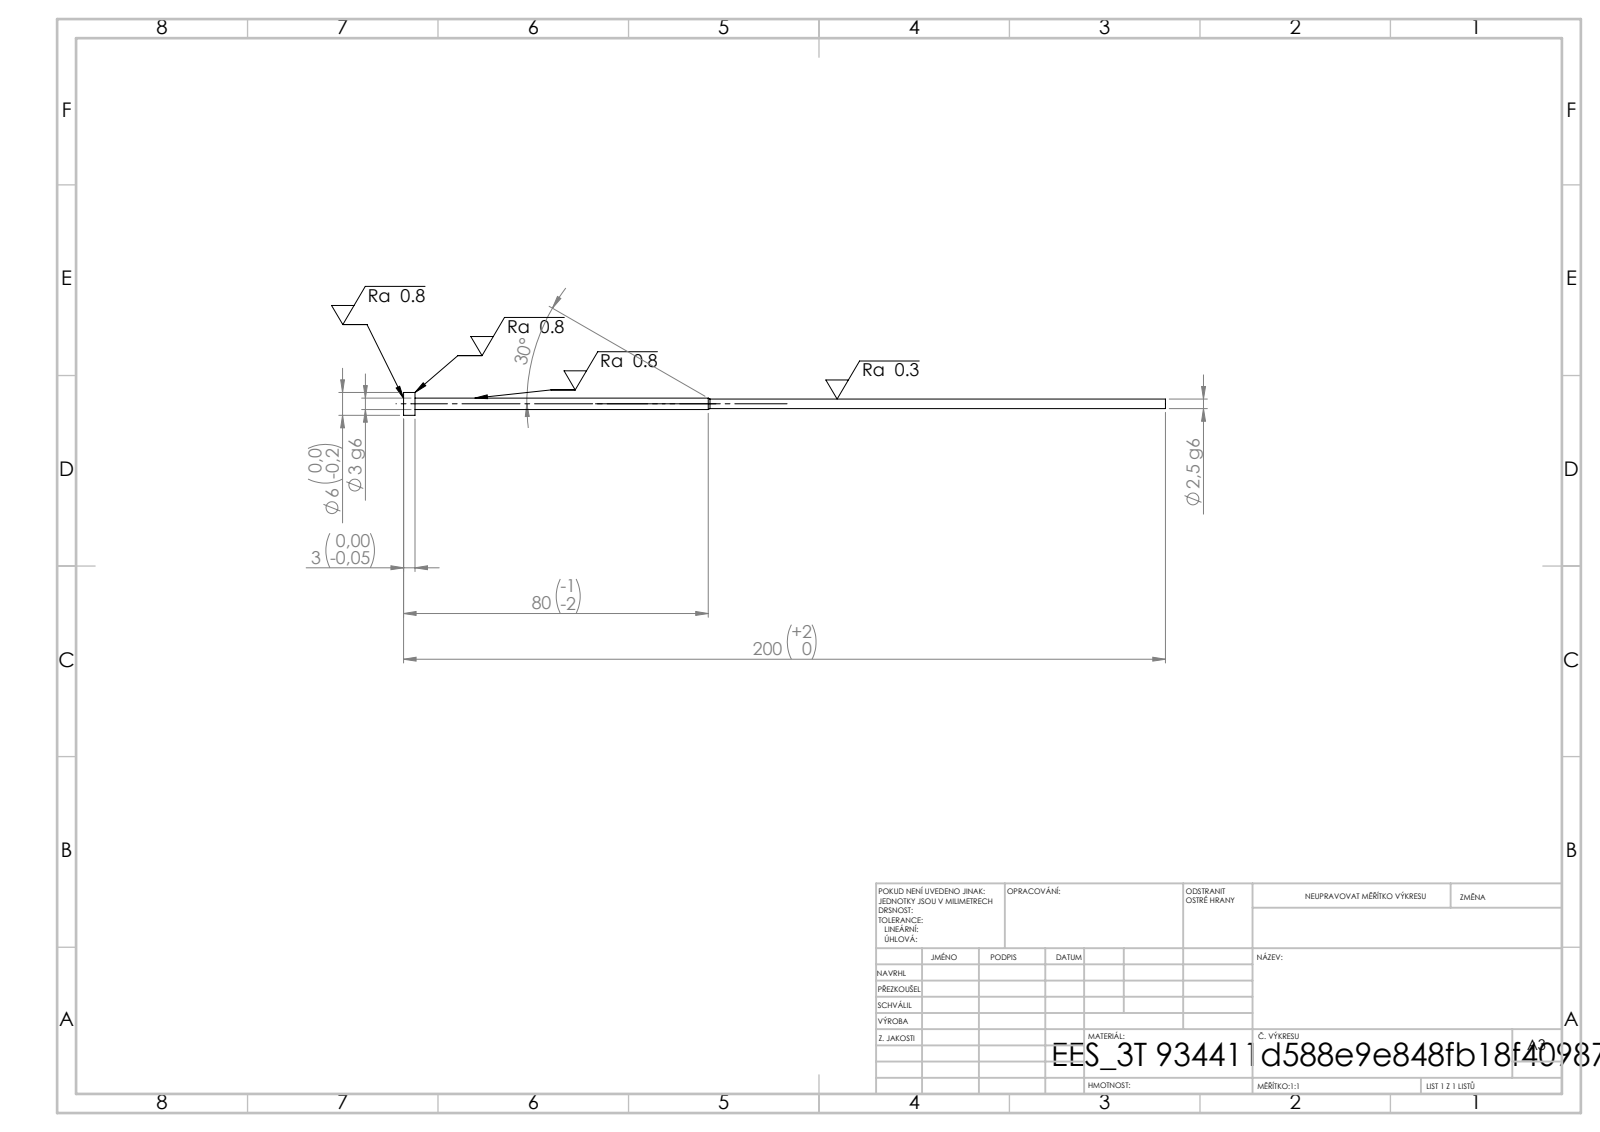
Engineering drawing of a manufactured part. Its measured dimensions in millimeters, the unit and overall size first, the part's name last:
Units: millimetres
Overall size (bounding box): 200 × 6 × 6
Round bosses / shafts (diameter × count): ⌀6 ×1, ⌀3 ×1, ⌀2.5 ×1
Main face-to-face distances: 3, 197, 200
Volume: 1 219 mm³ · Surface area: 1 780 mm²
Bodies: 1 solid, 11 faces (3 planar, 6 cylindrical, 2 other)
STEP written by: SolidWorks 2019 (CONFIG_CONTROL_DESIGN)
